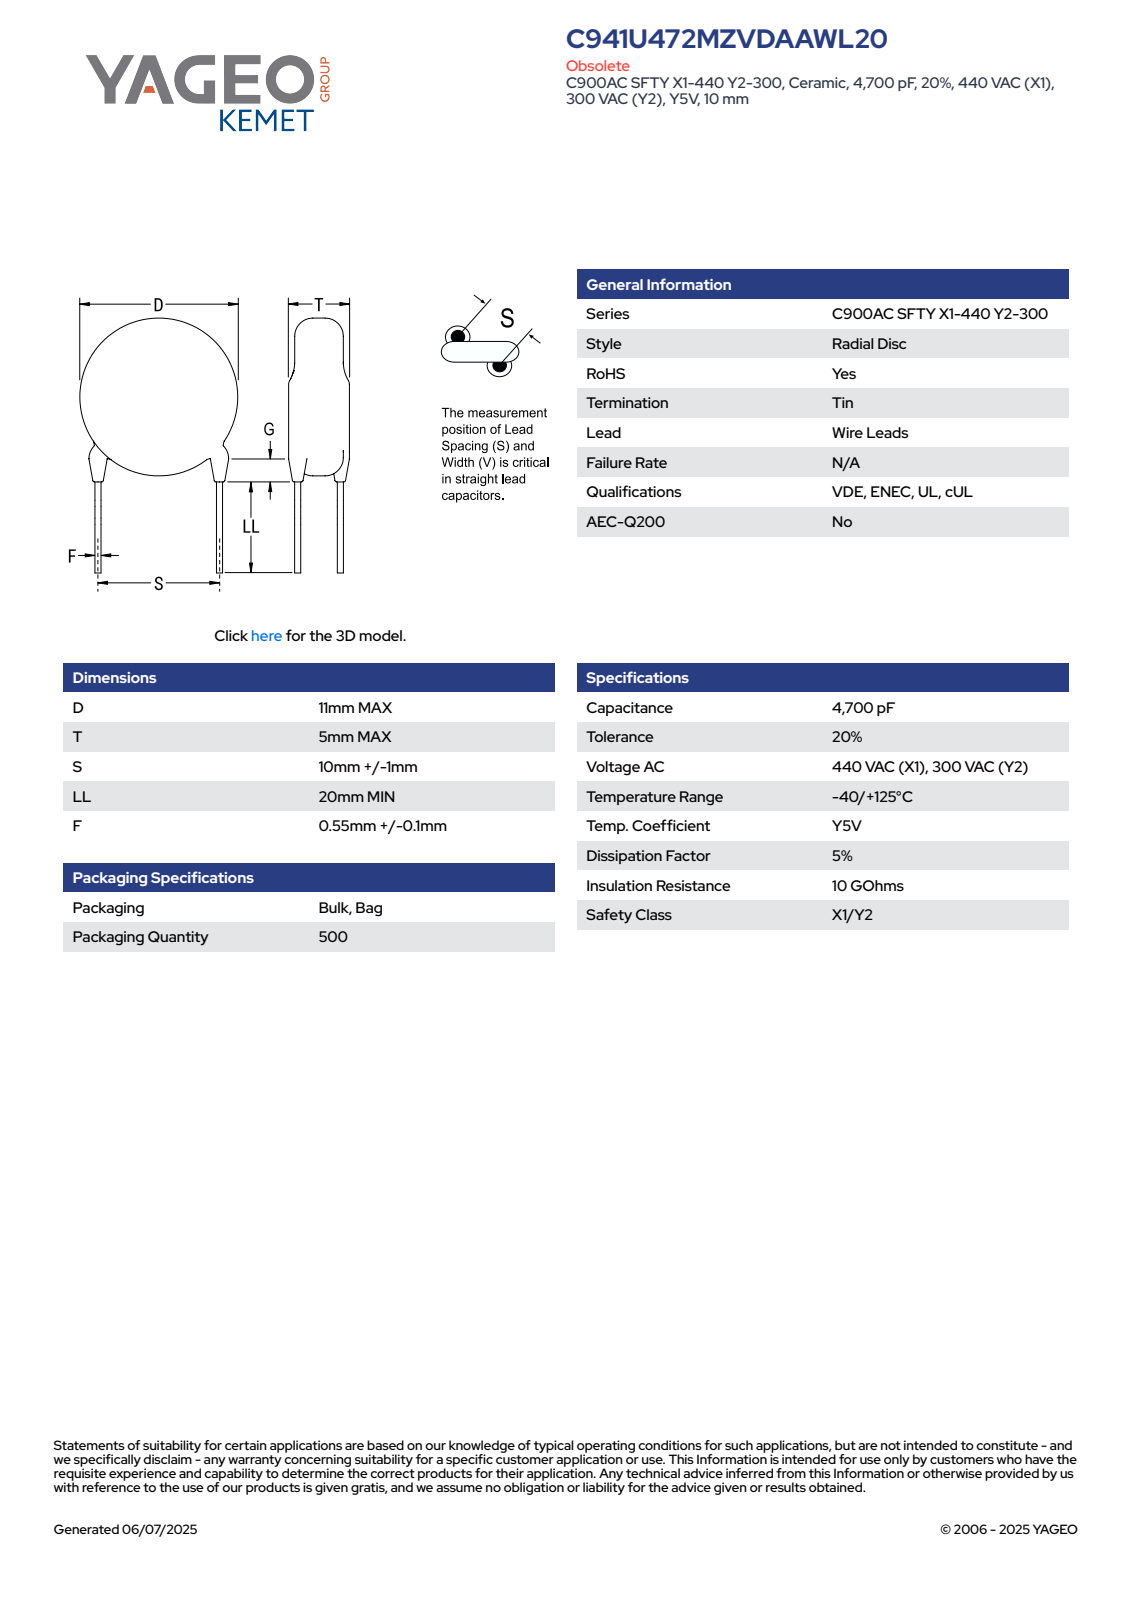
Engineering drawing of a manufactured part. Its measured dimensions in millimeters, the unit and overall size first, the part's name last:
Units: millimetres
Overall size (bounding box): 31.35 × 11 × 5
Round bosses / shafts (diameter × count): ⌀0.65 ×2, ⌀11 ×1
Main face-to-face distances: 5, 1.27, 26.48, 25.21, 0.35, 1.03, 5.19, 0.79, 3.77, 3.92
Volume: 478 mm³ · Surface area: 436 mm²
Bodies: 4 solids, 83 faces (61 planar, 6 cylindrical, 16 other)
Part name (STEP PRODUCT): CCD_STC900_D11T5S10LL20F0.65G3
STEP written by: SolidWorks 2014 (AUTOMOTIVE_DESIGN)
